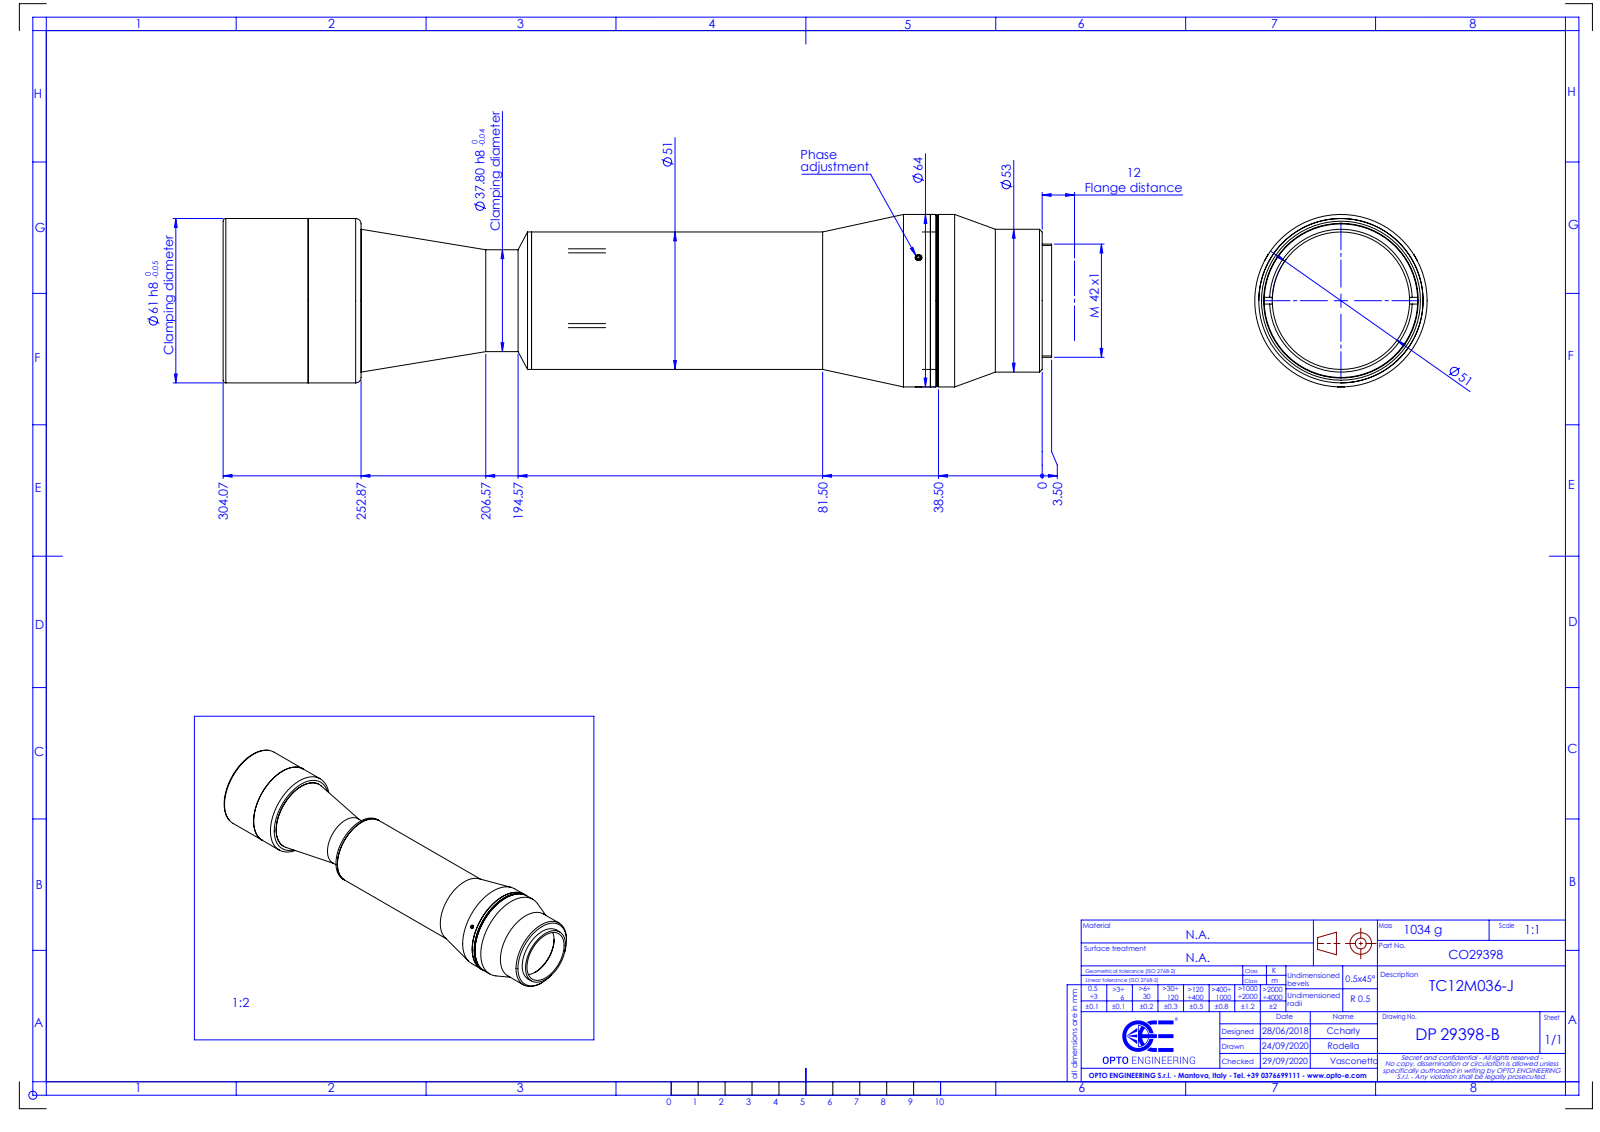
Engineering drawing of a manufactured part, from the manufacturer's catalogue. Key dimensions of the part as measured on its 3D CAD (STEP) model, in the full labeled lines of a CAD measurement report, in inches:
Part name (STEP PRODUCT): DP29398_TC12M036-J
STEP written by: SolidWorks 2021 (CONFIG_CONTROL_DESIGN)
Units: inches
Bodies: 0 solids, 103 faces (41 planar, 36 cylindrical, 26 other)
Overall size (bounding box): 12.109 × 2.52 × 2.52
Round holes (diameter × count): ⌀1.535 ×1, ⌀1.772 ×1, ⌀2.244 ×1
Round bosses / shafts (diameter × count): ⌀2.52 ×1, ⌀2.5 ×1, ⌀2.402 ×1, ⌀2.087 ×1, ⌀2.008 ×1, ⌀1.654 ×1, ⌀1.488 ×1
Main face-to-face distances: 9.094, 9.173, 0.079, 0.039, 9.213, 0.118, 3.265, 5.83, 5.908, 5.948
